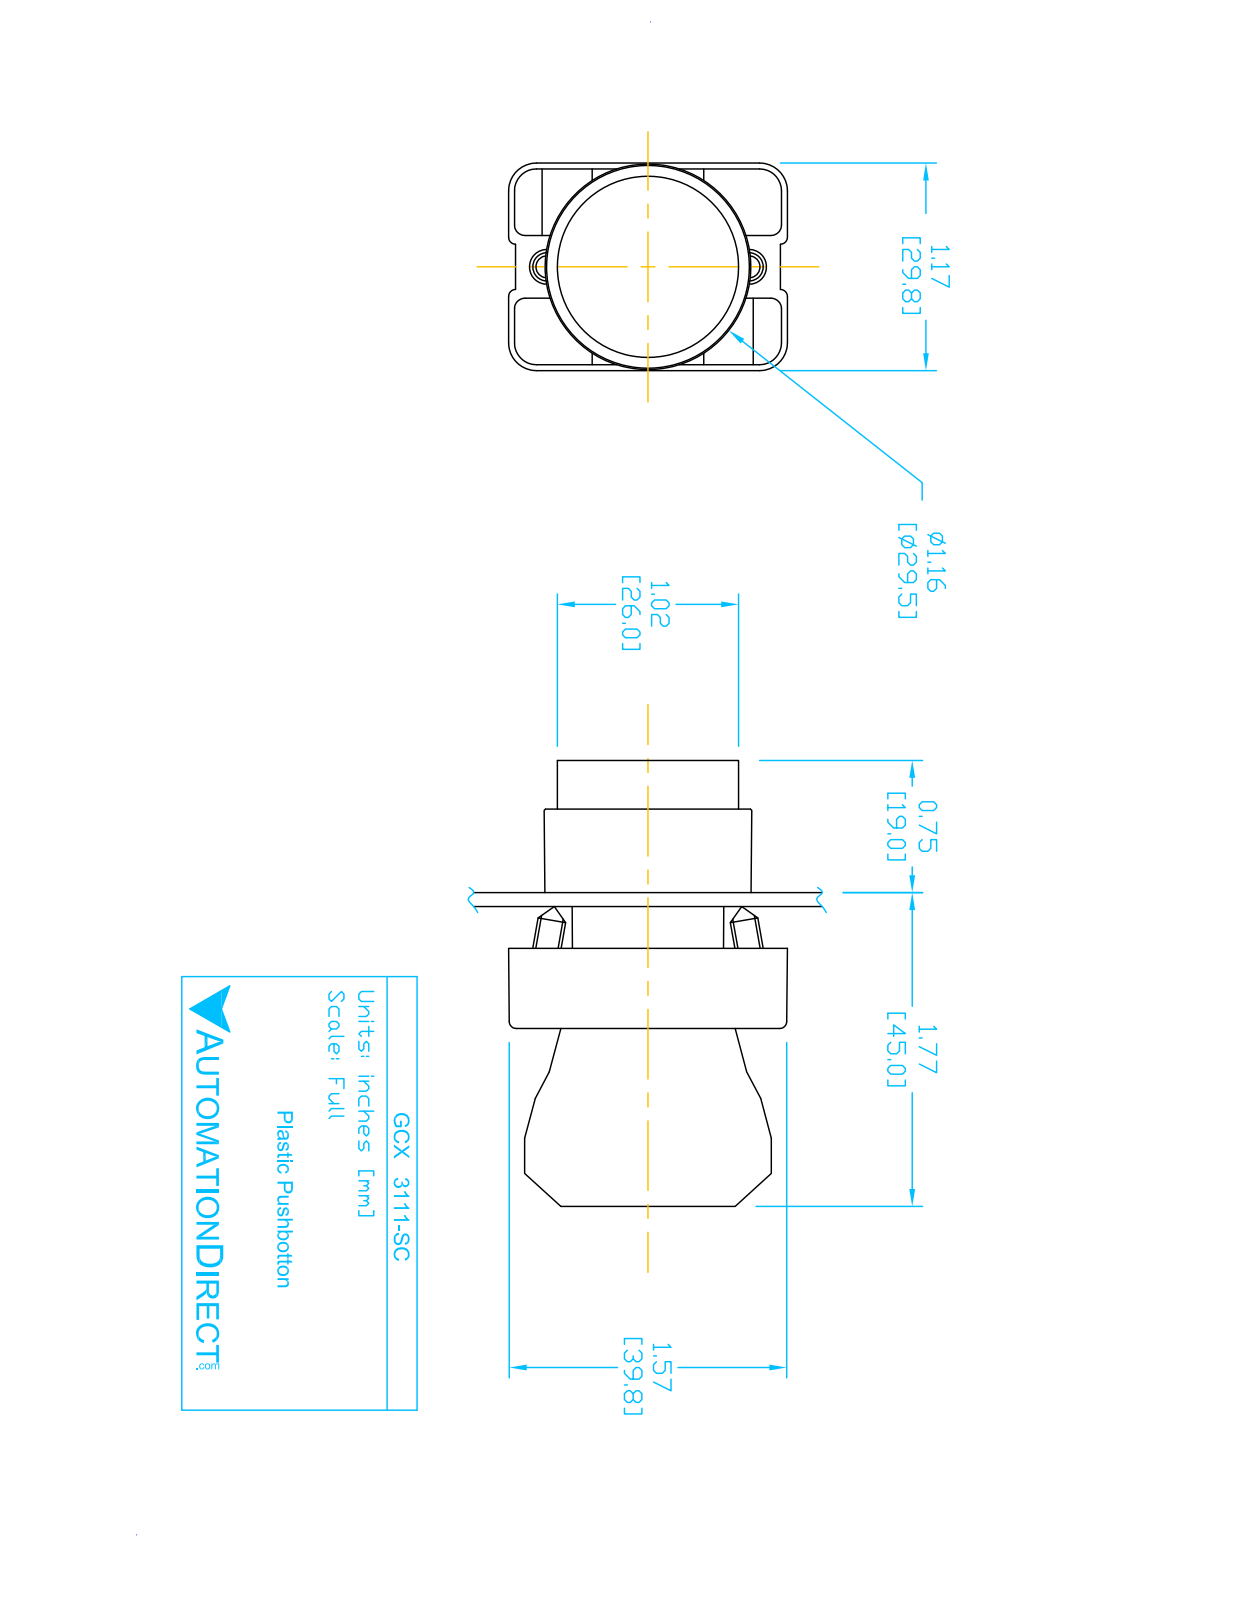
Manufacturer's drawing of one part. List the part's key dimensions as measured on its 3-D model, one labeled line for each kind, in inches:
Part name (STEP PRODUCT): ECX3029-2; GCX3111 OPERATOR; GCX3111-SC
STEP written by: SolidWorks 2016 (AUTOMOTIVE_DESIGN)
Units: inches
Bodies: 5 solids, 290 faces (147 planar, 118 cylindrical, 25 other)
Overall size (bounding box): 1.683 × 1.581 × 1.177
Volume: 0.933 in³ · Surface area: 19.73 in²
Round holes (diameter × count): ⌀0.124 ×2, ⌀0.13 ×2, ⌀0.197 ×1, ⌀0.878 ×1, ⌀0.888 ×1, ⌀1.024 ×1
Round bosses / shafts (diameter × count): ⌀0.157 ×2, ⌀1.175 ×1, ⌀1.004 ×1, ⌀0.945 ×1, ⌀0.856 ×1, ⌀0.78 ×1
Partial cylindrical surfaces — rounded edges, fillets, slot ends (radius × count): R0.059 ×24, R0.041 ×12, R0.124 ×12, R0.157 ×12, R0.039 ×4, R0.128 ×2, R0.392 ×1, R0.398 ×1
Main face-to-face distances: 0.033, 1.193, 0.031, 0.72, 0.472, 0.689, 1.161, 1.469, 1.437, 0.748
